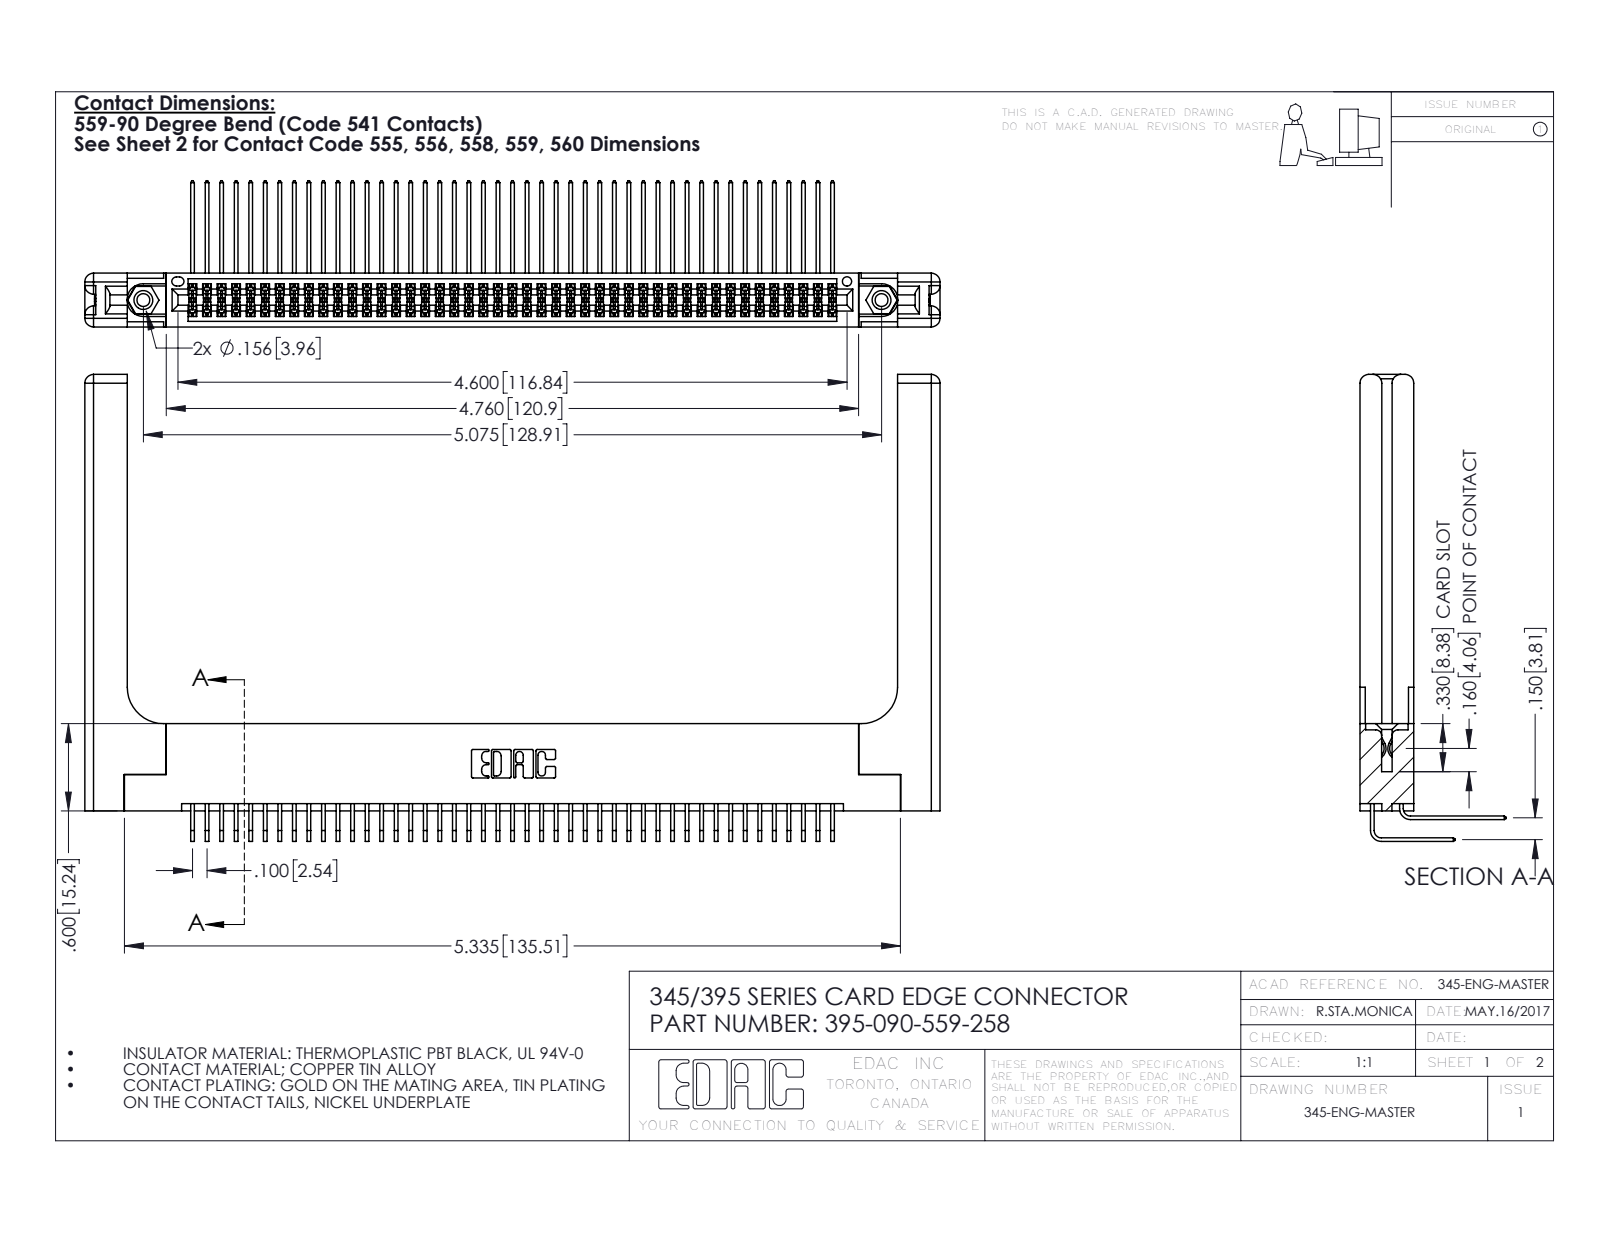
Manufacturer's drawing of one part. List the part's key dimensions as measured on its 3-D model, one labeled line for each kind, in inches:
Part name (STEP PRODUCT): 345-220-058_345-220-058; 345 Part_Flush Mounting Lugs - 0.156 Dia-TH; 345-292-001_559 Tail - 2; 345-292-001_558 559 Tail - 1 (+2 more)
STEP written by: SolidWorks 2016 (CONFIG_CONTROL_DESIGN)
Units: inches
Bodies: 95 solids, 5062 faces (3378 planar, 1624 cylindrical, 60 other)
Overall size (bounding box): 5.879 × 3.209 × 1.005
Volume: 1.436 in³ · Surface area: 46.2 in²
Round holes (diameter × count): ⌀0.089 ×2, ⌀0.125 ×2, ⌀0.156 ×2, ⌀0.064 ×1
Round bosses / shafts (diameter × count): ⌀0.155 ×2
Partial cylindrical surfaces — rounded edges, fillets, slot ends (radius × count): R0.006 ×136, R0.01 ×22, R0.06 ×16, R0.007 ×6, R0.031 ×6, R0.026 ×3, R0.014 ×2, R0.019 ×2
Main face-to-face distances: 0.072, 0.298, 0.37, 0.2, 0.098, 0.272, 0.025, 0.225, 0.175, 0.15
Hole centre spacings: 0.27, 4.839, 5.075
